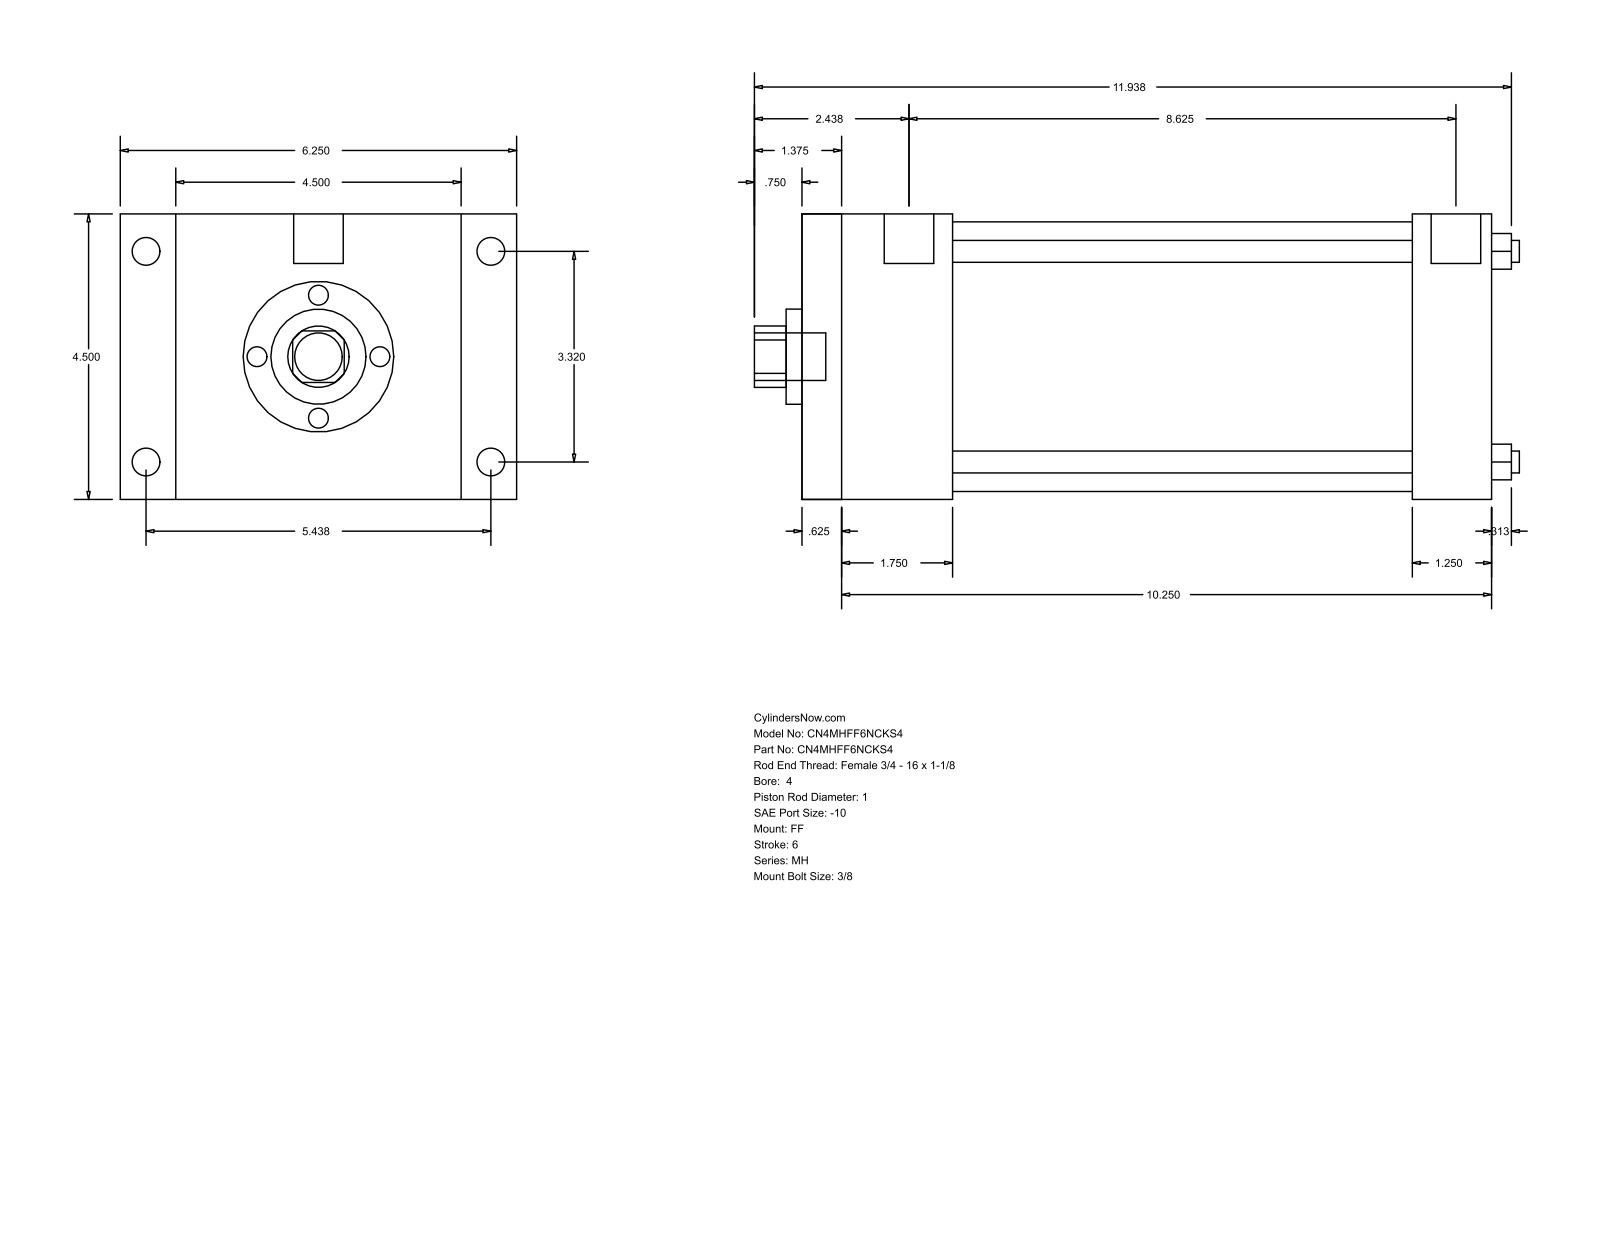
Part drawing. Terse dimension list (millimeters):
name: MH_FF__0400_1
written by: GSSL Pune (CONFIG_CONTROL_DESIGN)
unit: mm
bodies: 0 solids, 92 faces (64 planar, 28 cylindrical, 0 other)
size: 306.39 × 158.75 × 114.3
holes: 4× ⌀8.76, 1× ⌀25.4, 1× ⌀38.1, 1× ⌀107.95
bosses: 4× ⌀11.13, 4× ⌀8.73, 2× ⌀19.84, 1× ⌀19.05
rounds: 1× R12.29
face distances: 114.3, 276.22, 15.87, 260.35, 60.33, 44.46, 215.89, 244.47, 228.6, 184.14
hole spacings: 59.62, 84.32, 119.25
